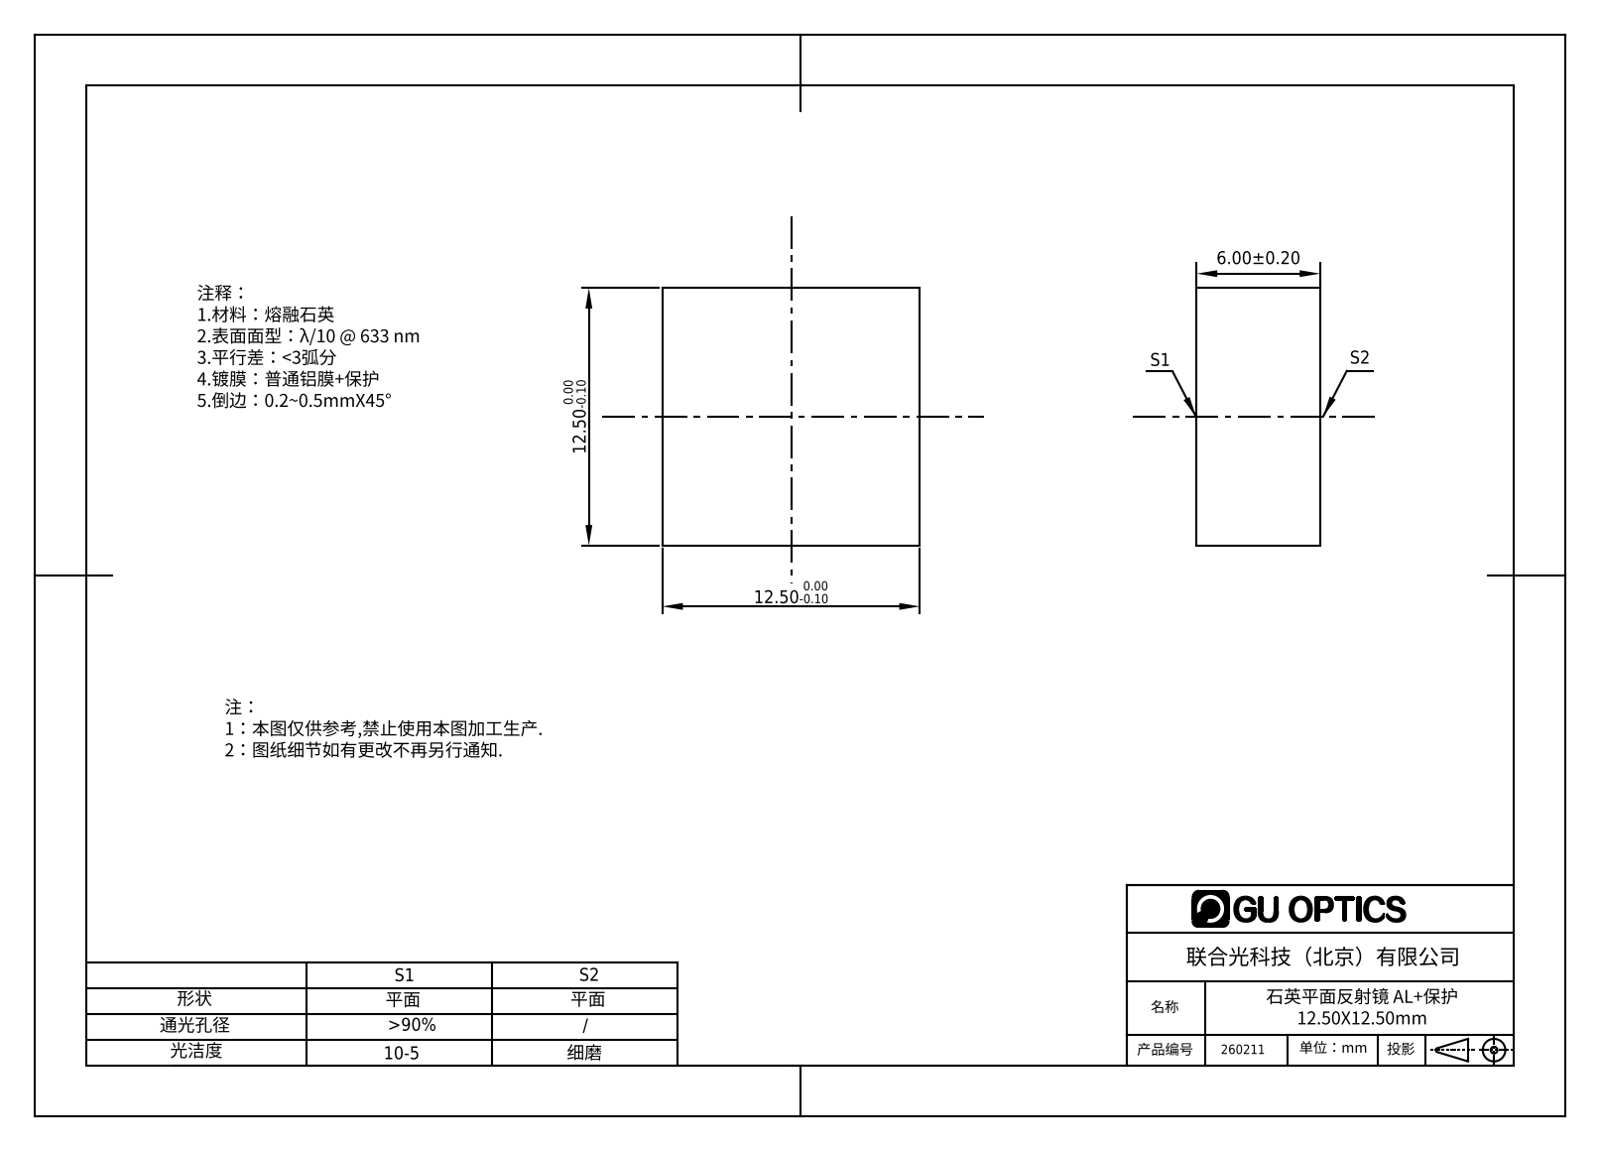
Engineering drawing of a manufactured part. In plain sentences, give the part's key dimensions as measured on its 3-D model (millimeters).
The part is named "260069". Its 3-D file was written by "SolidWorks 2016 (AUTOMOTIVE_DESIGN)". It is 1 solid with 6 faces: 6 planar, 0 cylindrical and 0 other. Overall it measures 12.5 by 12.5 by 6 millimeters. Its volume is 938 cubic millimeters and its surface area 612 square millimeters. The main face-to-face distances are 6, 12.5.
